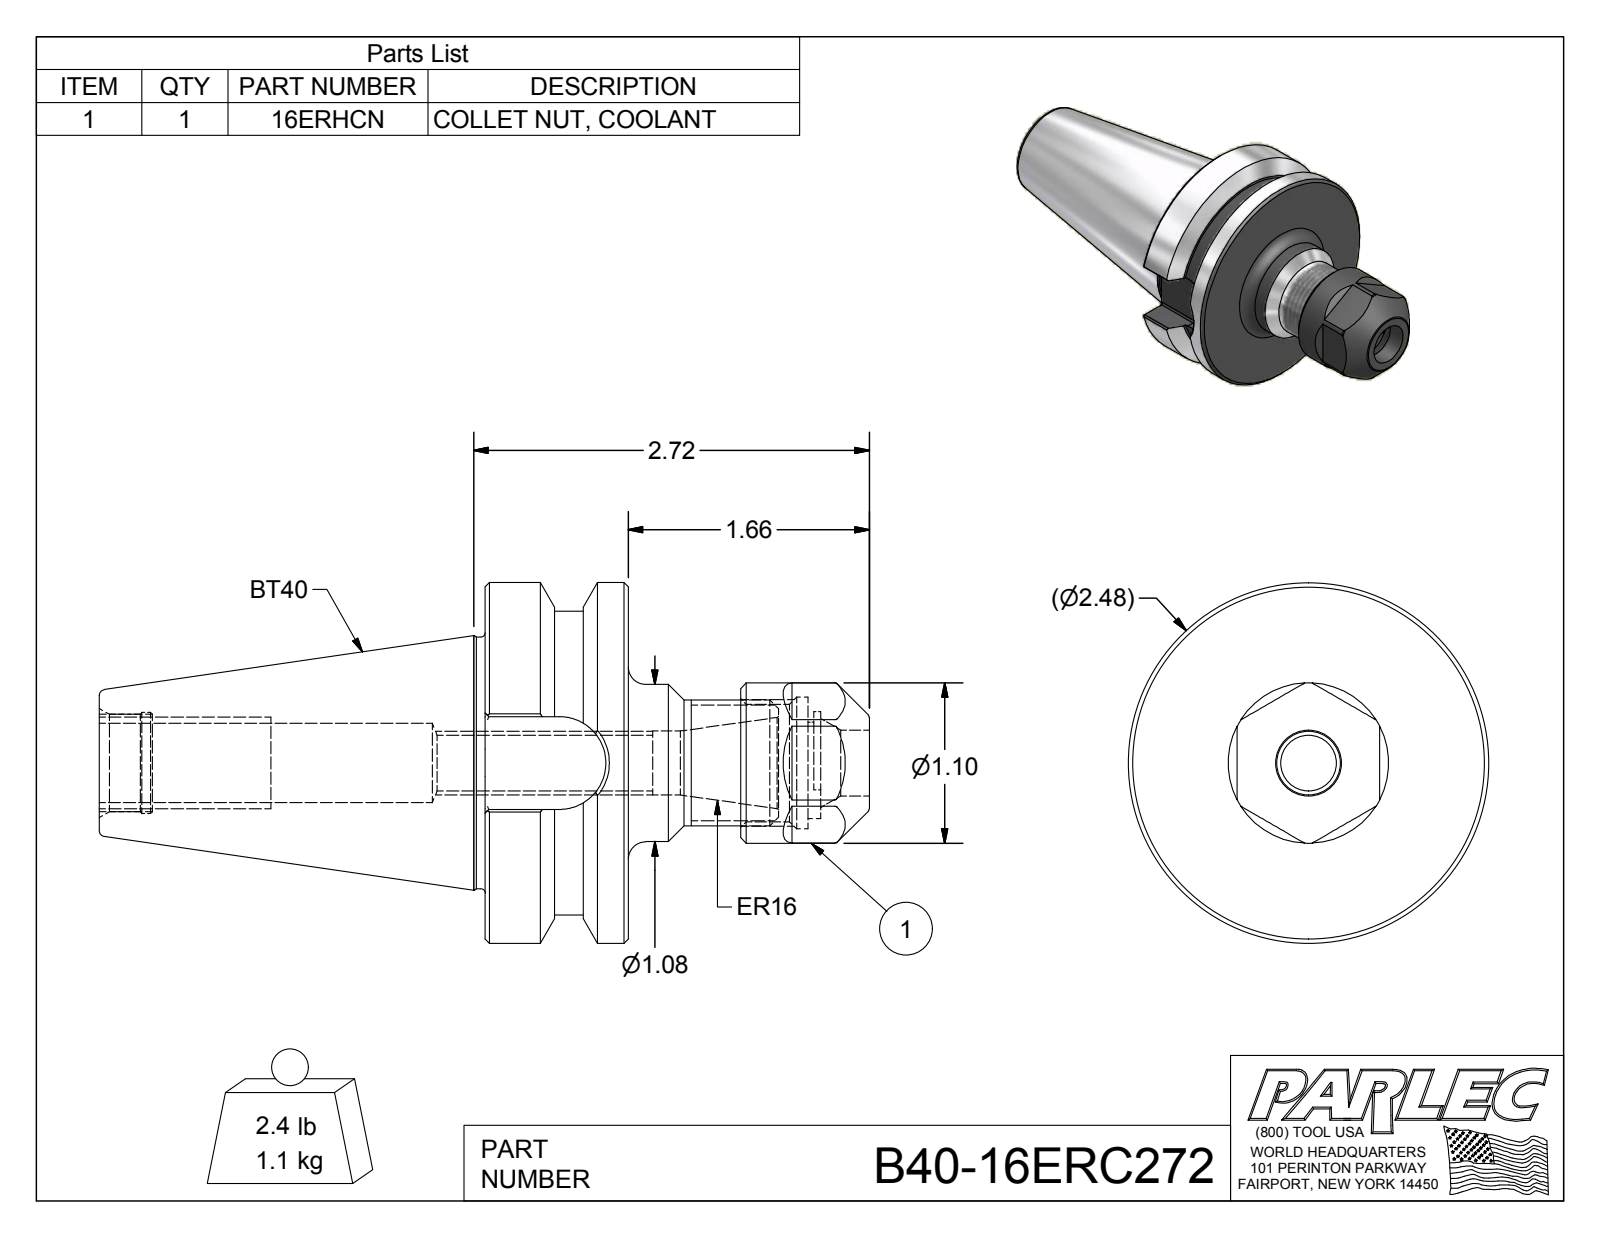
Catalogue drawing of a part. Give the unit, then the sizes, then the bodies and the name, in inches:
Units: inches
Overall size (bounding box): 5.295 × 2.48 × 2.48
Round holes (diameter × count): ⌀0.383 ×1, ⌀0.44 ×1, ⌀0.453 ×1, ⌀0.545 ×1, ⌀0.661 ×1, ⌀0.67 ×1, ⌀0.694 ×1, ⌀0.807 ×1, ⌀0.906 ×1
Round bosses / shafts (diameter × count): ⌀2.48 ×1, ⌀2.087 ×1, ⌀1.73 ×1, ⌀1.102 ×1, ⌀1.08 ×1, ⌀0.866 ×1, ⌀0.669 ×1
Partial cylindrical surfaces — rounded edges, fillets, slot ends (radius × count): R0.02 ×8, R0.319 ×1, R0.354 ×1
Main face-to-face distances: 0.984, 0.979, 1.78, 2.653, 3.637, 0.401, 1.38, 4.874, 2.221, 1.237
Hole centre spacings: 0.051
Volume: 8.397 in³ · Surface area: 45.54 in²
Bodies: 2 solids, 108 faces (42 planar, 30 cylindrical, 36 other)
Part name (STEP PRODUCT): B40-16ERC272; B40-16ER2-1; 16ERHCN
STEP written by: Autodesk Inventor 2012 (AUTOMOTIVE_DESIGN)
